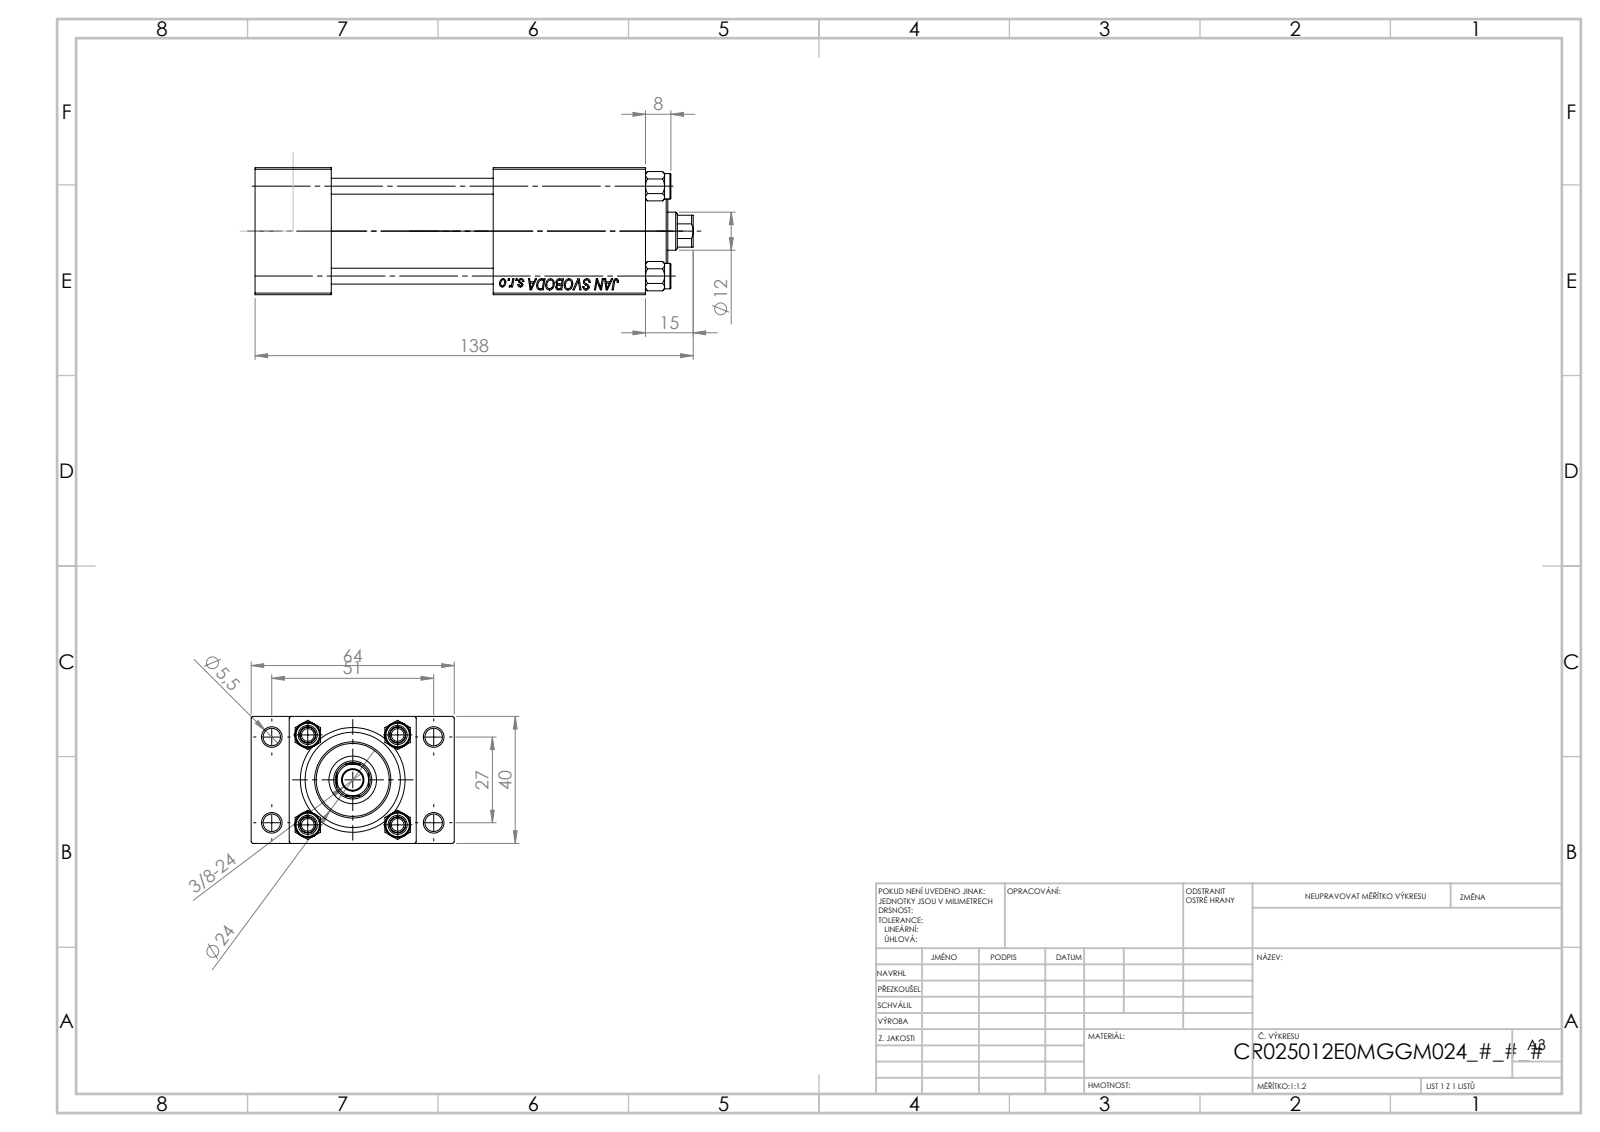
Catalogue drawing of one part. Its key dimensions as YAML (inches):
part_name: "V215CR_VCP_E; V215_VC_A; V215CR_TYCINKA_E; V215CR_E_Body (+1 more)"
step_written_by: "SolidWorks 2019 (CONFIG_CONTROL_DESIGN)"
units: inches
bodies: {solids: 11, faces: 1136, planar: 497, cylindrical: 87, other: 552}
overall_size: [5.433, 2.52, 1.575]
volume: 10.11
surface_area: 97.98
round_holes:
  - {diameter: 0.197, count: 4}
  - {diameter: 0.217, count: 4}
  - {diameter: 0.787, count: 3}
  - {diameter: 0.276, count: 2}
  - {diameter: 0.518, count: 2}
  - {diameter: 0.256, count: 1}
  - {diameter: 0.472, count: 1}
  - {diameter: 0.591, count: 1}
  - {diameter: 0.984, count: 1}
  - {diameter: 1.181, count: 1}
round_bosses_or_shafts:
  - {diameter: 0.315, count: 4}
  - {diameter: 1.22, count: 1}
  - {diameter: 0.945, count: 1}
partial_cylinders:
  - {radius: 0.217, count: 1}
face_to_face_distances: [1.575, 0.945, 0.472, 2.047, 2.008, 4.843, 3.898, 3.713, 2.768, 1.13]
hole_center_spacings: [0.448, 0.788, 1.114, 1.136, 1.177, 1.561, 1.903, 1.063]
